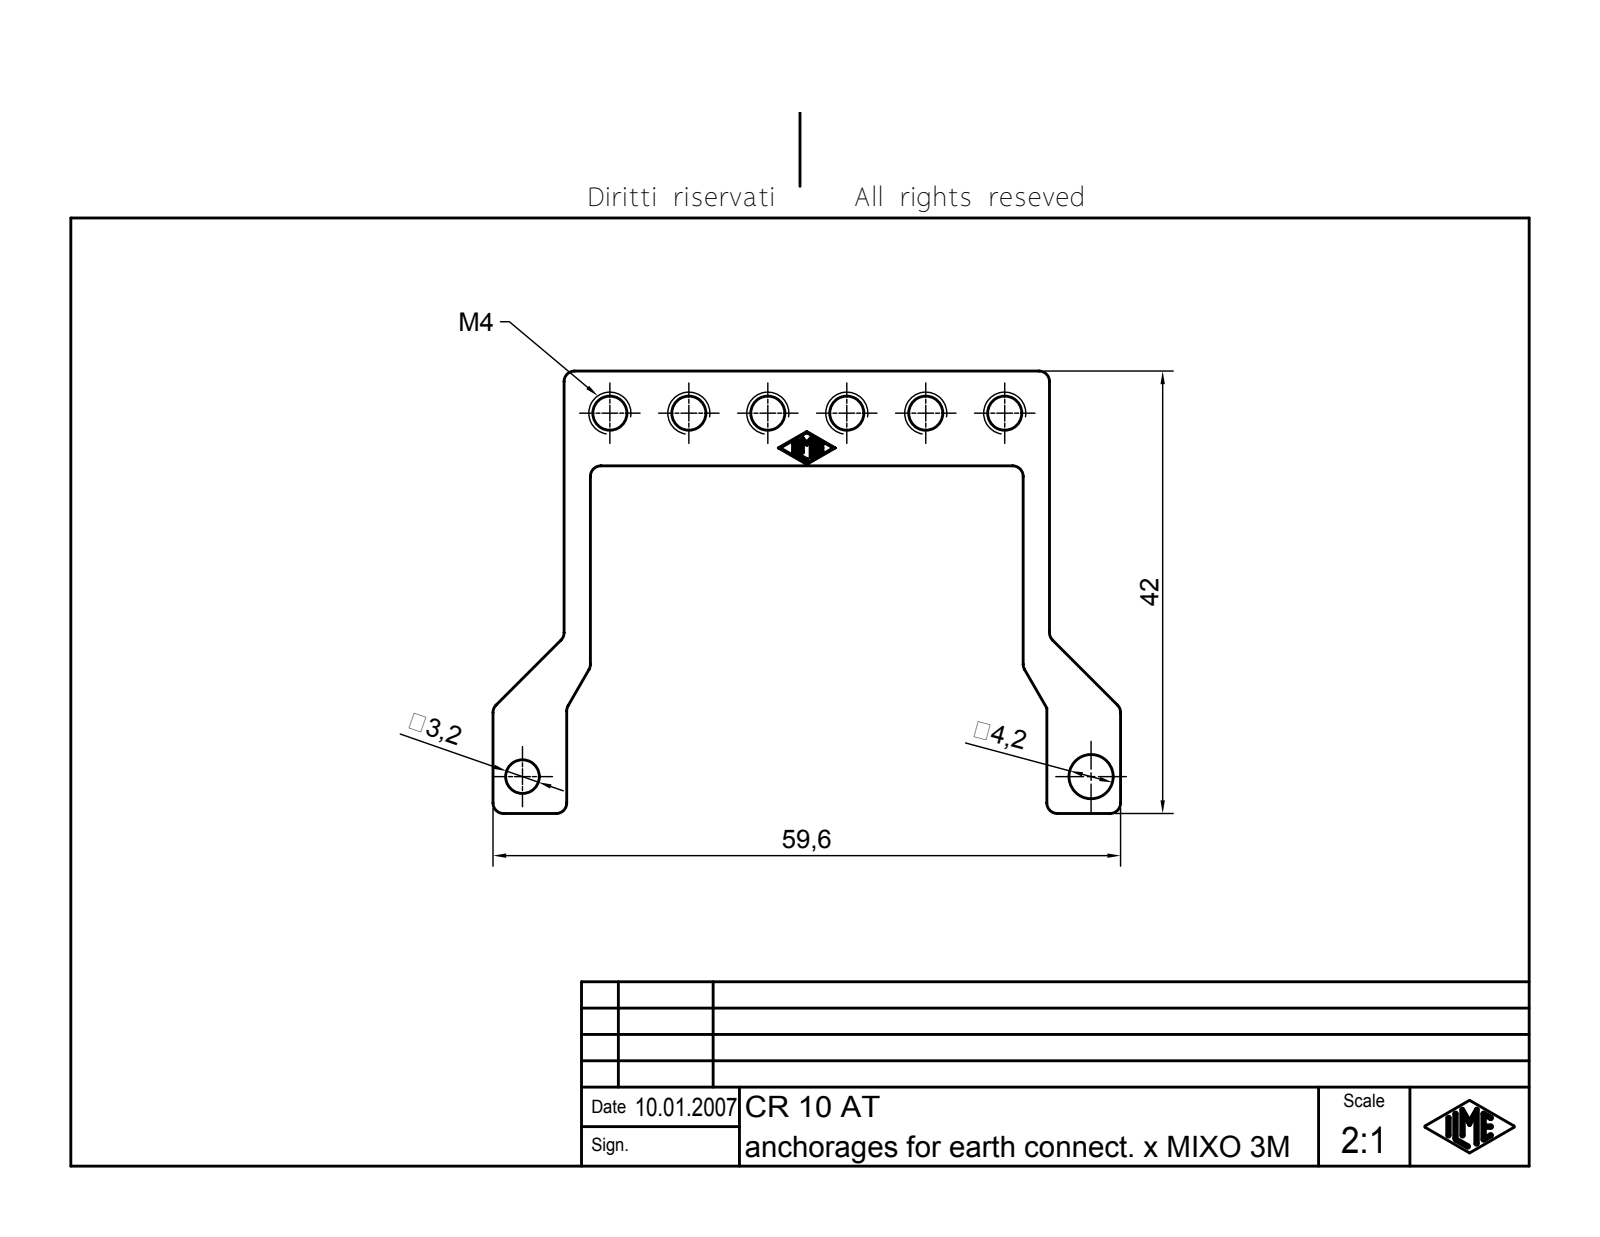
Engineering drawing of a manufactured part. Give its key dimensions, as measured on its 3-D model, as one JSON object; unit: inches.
{"part_name": "CR 10 AT", "step_written_by": "Autodesk Inventor 7 (AUTOMOTIVE_DESIGN)", "units": "inches", "bodies": {"solids": 1, "faces": 115, "planar": 55, "cylindrical": 48, "other": 12}, "overall_size": [2.346, 1.654, 0.079], "volume_in3": 0.077, "surface_area_in2": 3.032, "round_holes": [[0.126, 1], [0.165, 1]], "partial_cylinders_radius": [[0.039, 15], [0.004, 14]], "face_to_face_distances": [0.079, 0.354, 0.098, 1.717, 1.815, 1.618, 1.805, 0.089, 1.707, 0.266], "hole_center_spacings": [2.126]}
